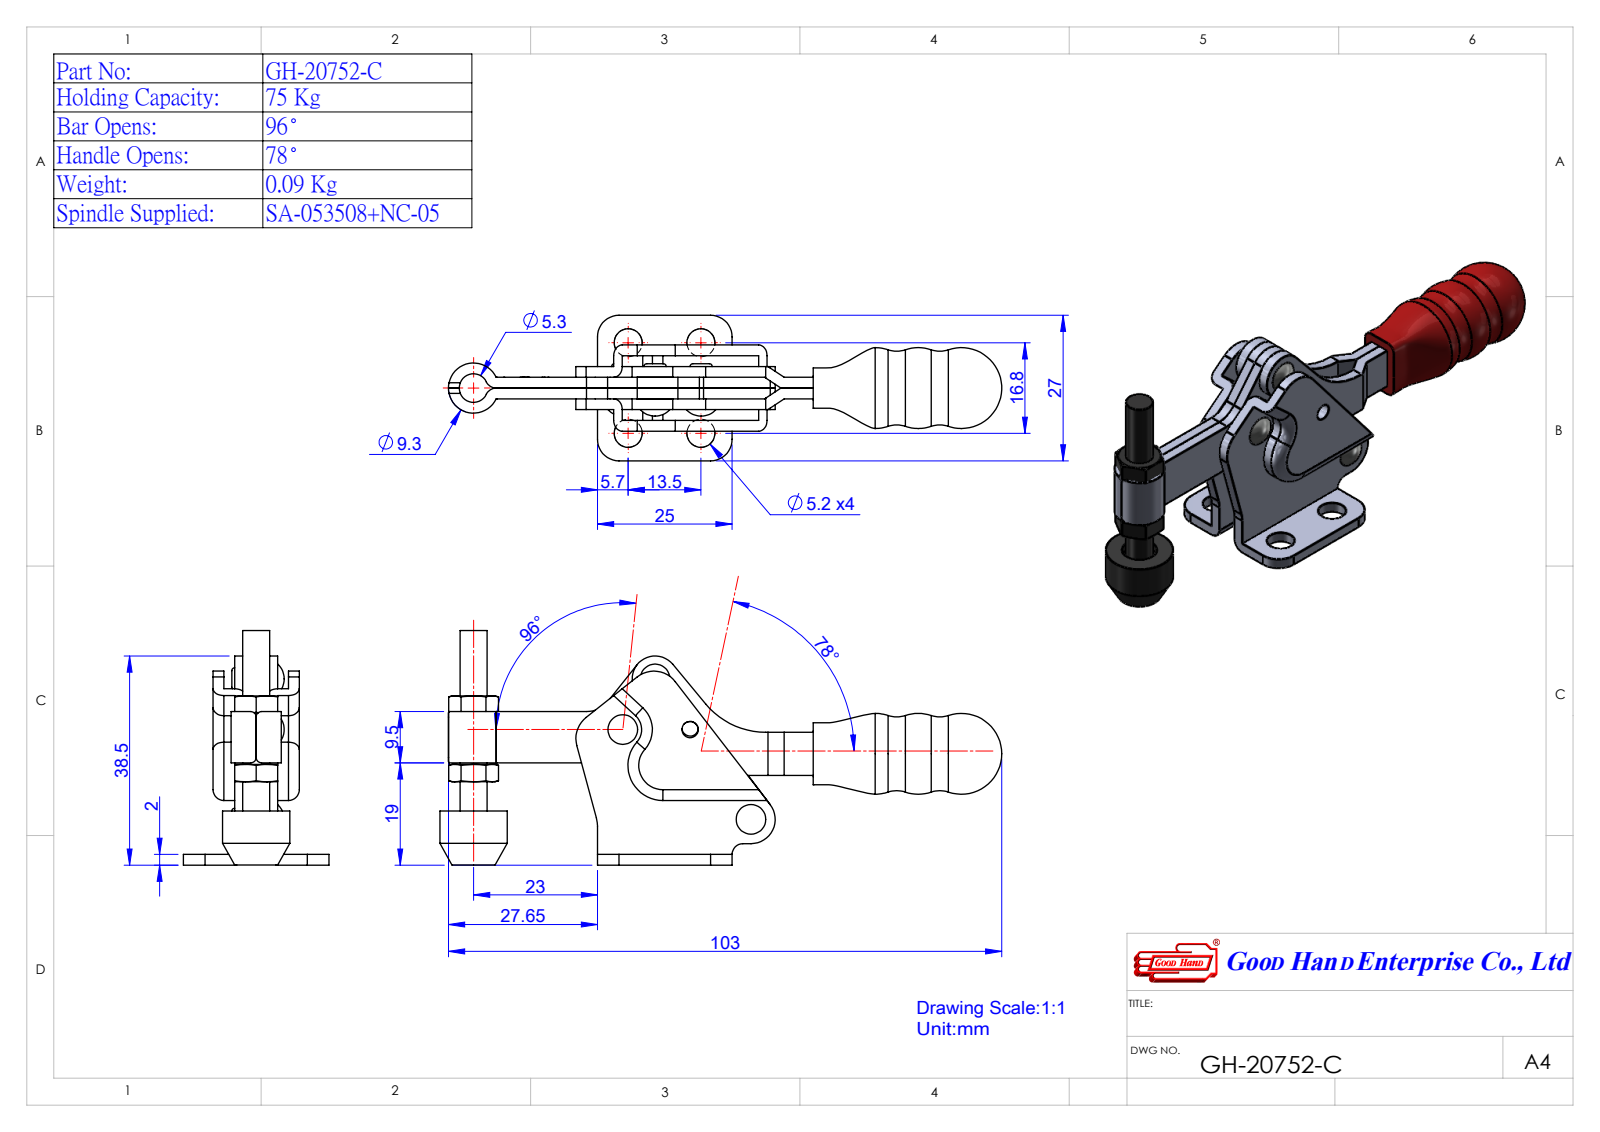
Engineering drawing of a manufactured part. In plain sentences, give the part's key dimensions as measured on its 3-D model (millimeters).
The part is named "Group3^GH-20752-C(簡化); Group4^GH-20752-C(簡化); GH-20752-C(簡化); Group2^GH-20752-C(簡化) (+2 more)". Its 3-D file was written by "SolidWorks 2016 (AUTOMOTIVE_DESIGN)". It is 5 solids with 270 faces: 100 planar, 112 cylindrical and 58 other. Overall it measures 102.3 by 43.54 by 27 millimeters. Its volume is 16 096 cubic millimeters and its surface area 12 897 square millimeters. Round holes: 5 of diameter 3, 5 of diameter 5.3, 4 of diameter 2.5. Round bosses or shafts: 2 of diameter 3, 1 of diameter 12.5, 1 of diameter 9.3, 1 of diameter 5. Partial cylindrical surfaces (rounded edges, fillets, slot ends): 5 of radius 1, 4 of radius 4, 4 of radius 5, 3 of radius 4.5, 2 of radius 2.01, 1 of radius 2, 1 of radius 3.5, 1 of radius 4.25. The main face-to-face distances are 2, 4, 6, 10, 8, 12, 14, 16, 9.5, 1.96. The hole center spacings are 12.5, 13.5, 16.8, 21.55, 29.9, 43.03, 0.33, 4.75.
